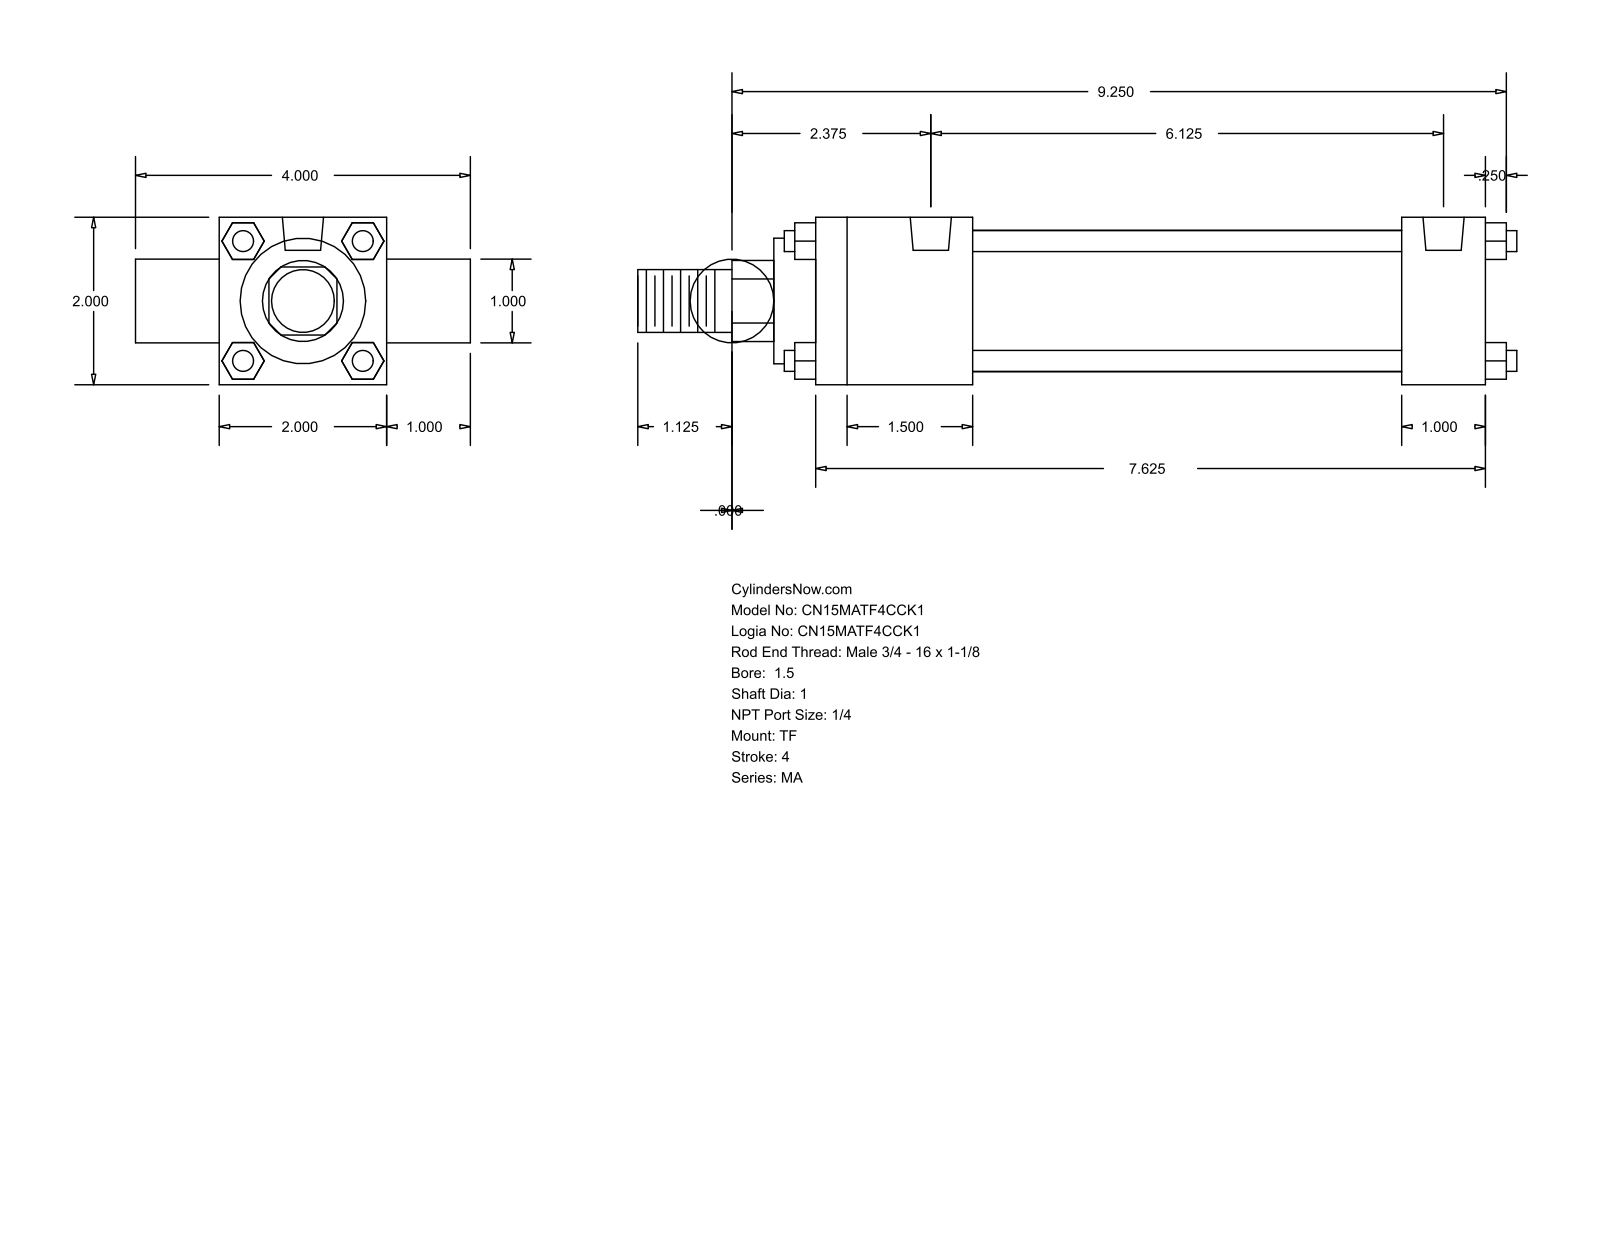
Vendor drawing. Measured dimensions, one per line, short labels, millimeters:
name: MA_TF__0150_1
written by: GSSL Pune (CONFIG_CONTROL_DESIGN)
unit: mm
bodies: 0 solids, 120 faces (92 planar, 28 cylindrical, 0 other)
size: 266.7 × 101.6 × 50.8
holes: 3× ⌀7.94, 2× ⌀12.49
bosses: 4× ⌀6.35, 2× ⌀25.4, 1× ⌀42.93, 1× ⌀38.1, 1× ⌀19.05
rounds: 1× R12.29
face distances: 50.8, 25.4, 203.2, 76.2, 6.35, 47.63, 177.8, 130.17, 155.57, 215.9
hole spacings: 155.57
